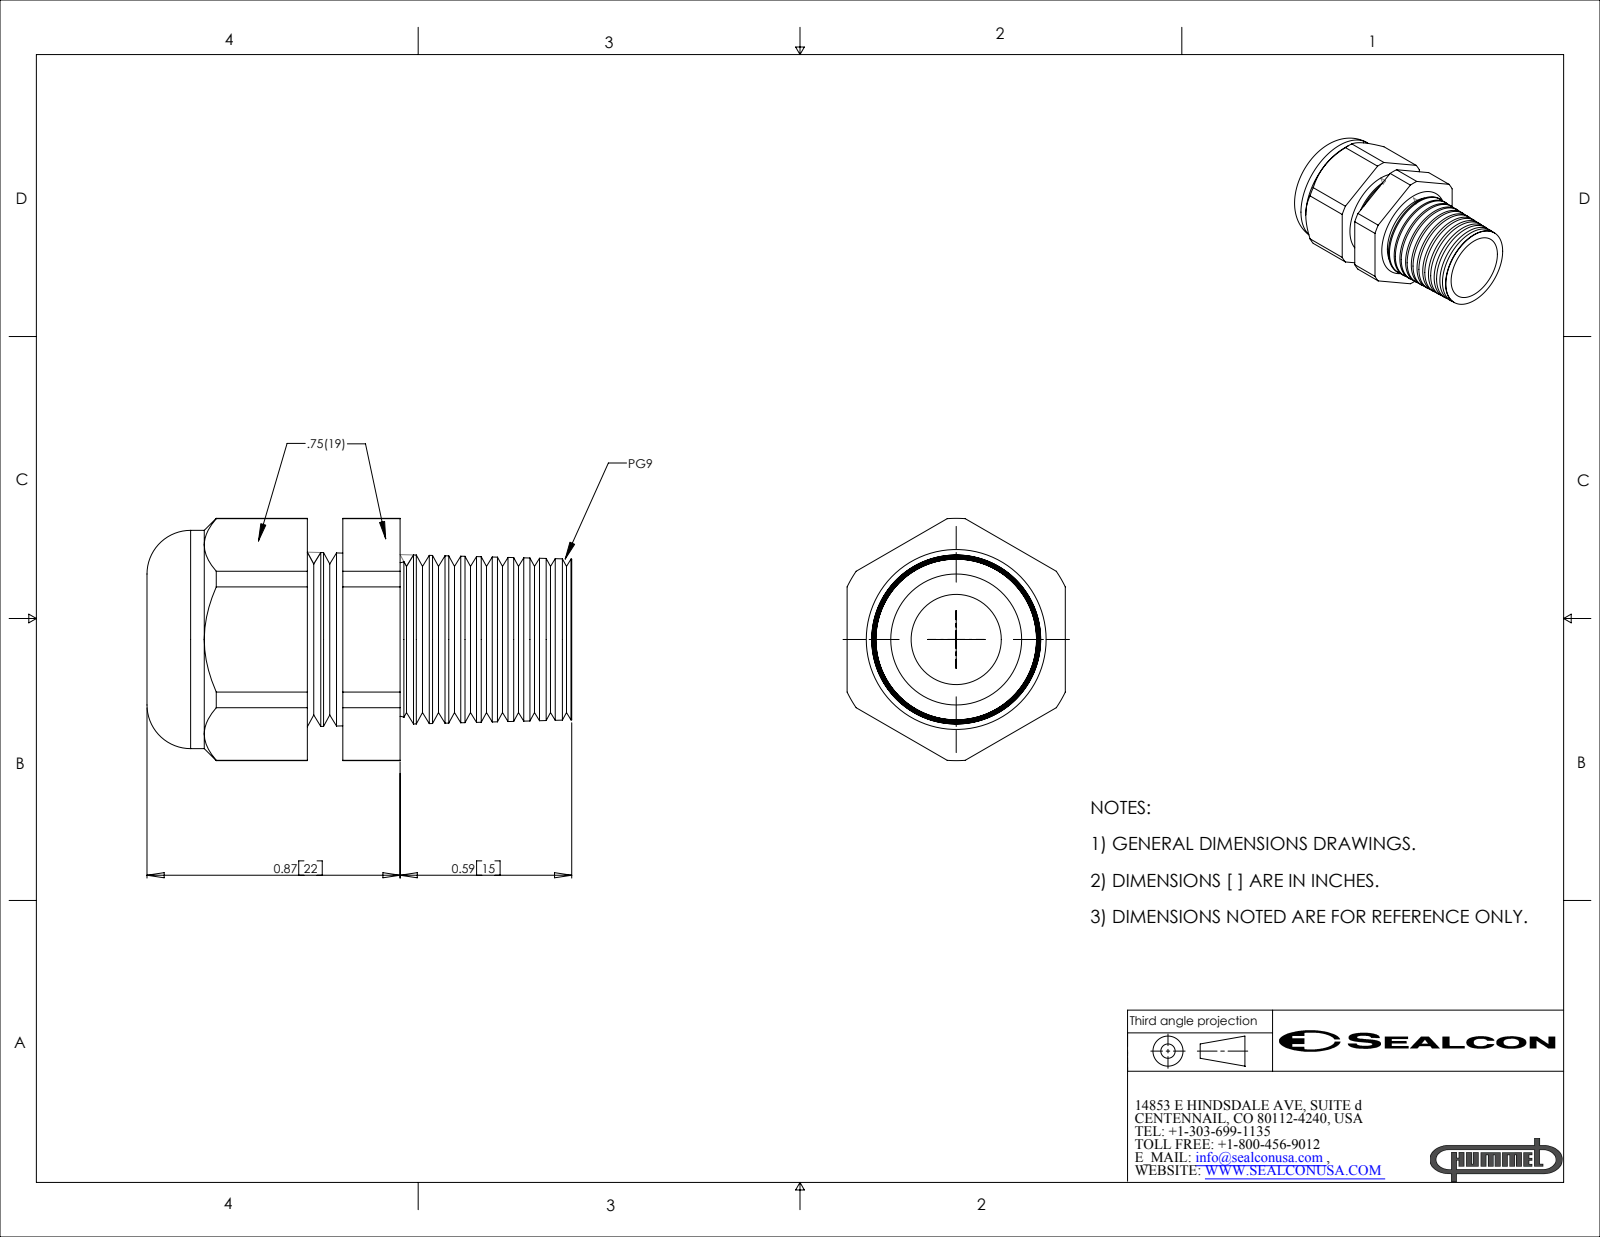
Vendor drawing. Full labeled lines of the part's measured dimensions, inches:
Part name (STEP PRODUCT): CD09CR-GY
STEP written by: SolidWorks 2007 (CONFIG_CONTROL_DESIGN)
Units: inches
Bodies: 2 solids, 135 faces (19 planar, 22 cylindrical, 94 other)
Overall size (bounding box): 1.46 × 0.833 × 0.75
Volume: 0.394 in³ · Surface area: 7.092 in²
Round holes (diameter × count): ⌀0.24 ×1, ⌀0.45 ×1
Round bosses / shafts (diameter × count): ⌀0.75 ×1
Partial cylindrical surfaces — rounded edges, fillets, slot ends (radius × count): R0.416 ×1
Main face-to-face distances: 0.75, 0.476, 0.354, 0.122, 0.75, 0.673, 0.319, 0.197, 0.167, 0.521
